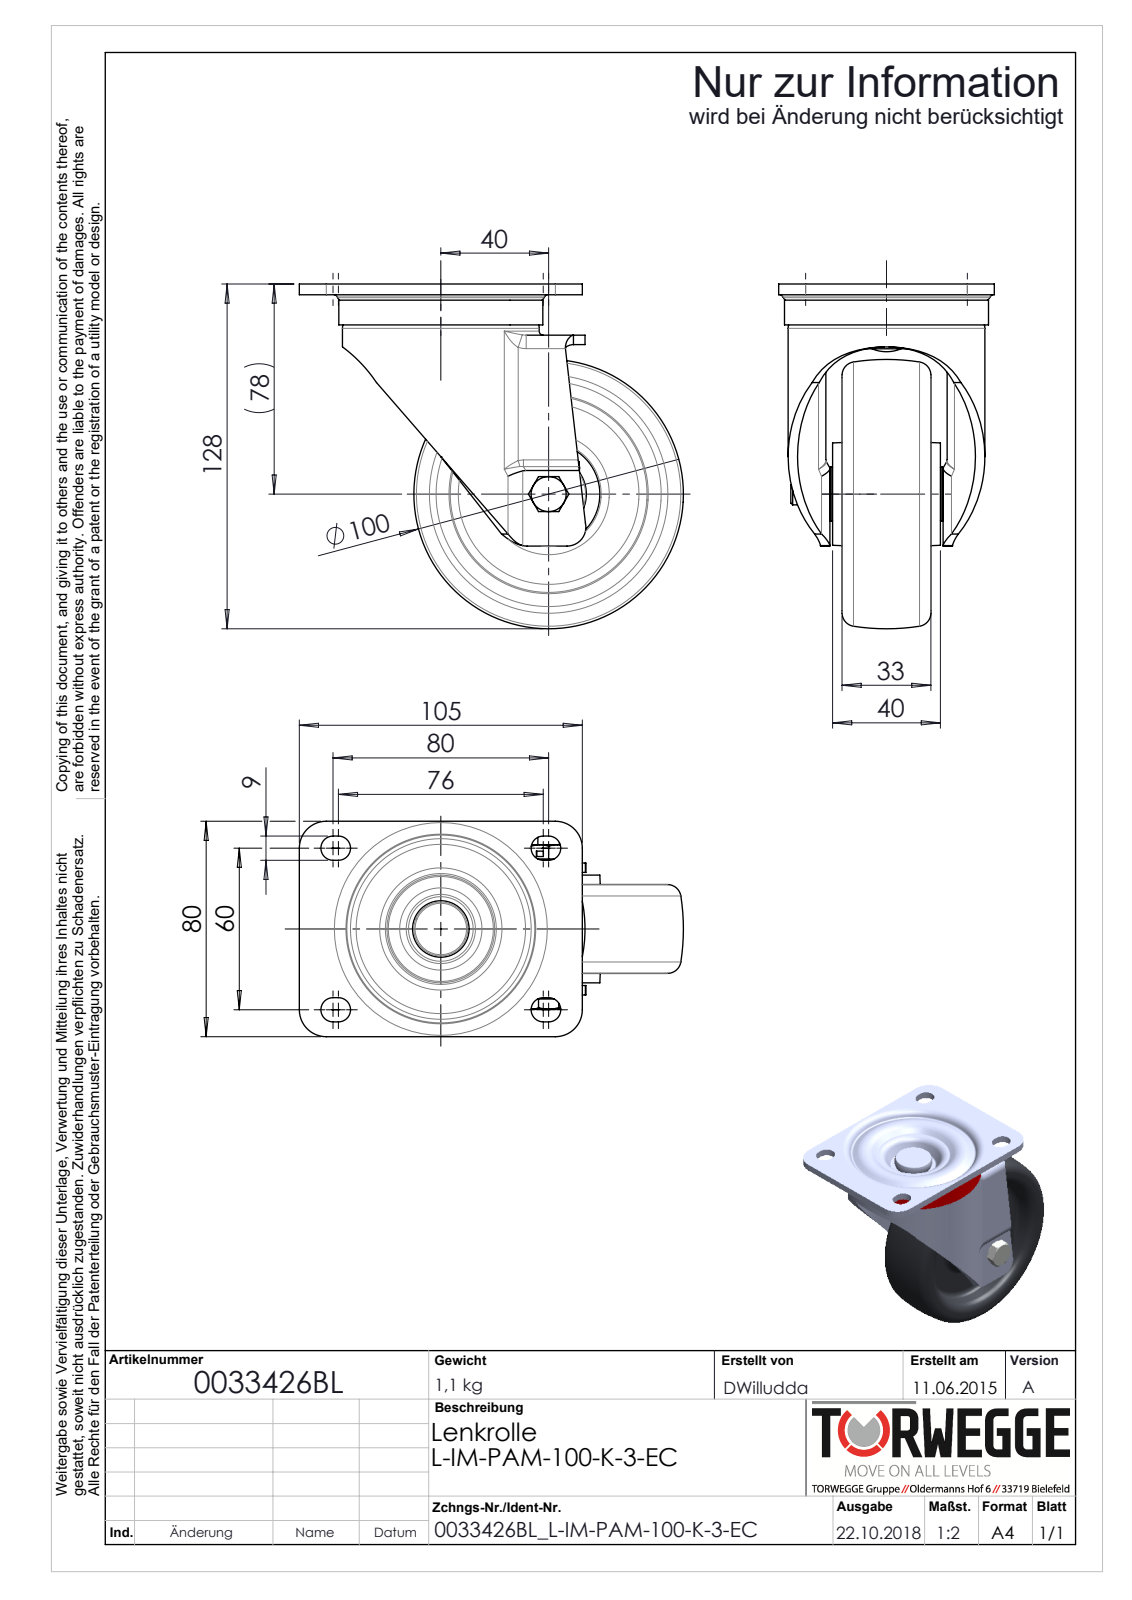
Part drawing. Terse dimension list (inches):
name: 0033426BL_L-IM-PAM-100-K-3-EC
written by: SolidWorks 2016 (AUTOMOTIVE_DESIGN)
unit: in
bodies: 20 solids, 788 faces (345 planar, 196 cylindrical, 247 other)
size: 5.61 × 5.039 × 3.15
volume: 18.11 in³; area: 190.4 in²
holes: 1× ⌀0.268, 1× ⌀0.315, 1× ⌀0.323, 1× ⌀0.335, 1× ⌀0.472, 1× ⌀0.488, 1× ⌀0.492, 1× ⌀0.661, 1× ⌀0.906, 1× ⌀0.913, 1× ⌀1.382, 1× ⌀1.398
bosses: 1× ⌀2.98, 1× ⌀2.874, 1× ⌀2.067, 1× ⌀1.102, 1× ⌀0.827, 1× ⌀0.787, 1× ⌀0.591, 1× ⌀0.512
rounds: 8× R0.015, 8× R0.177, 7× R0.008, 7× R0.024, 4× R0.005, 4× R0.034, 4× R0.037, 4× R0.059
face distances: 0.157, 0.138, 0.059, 0.039, 1.85, 0.689, 0.591, 0.197, 0.098, 0.551
